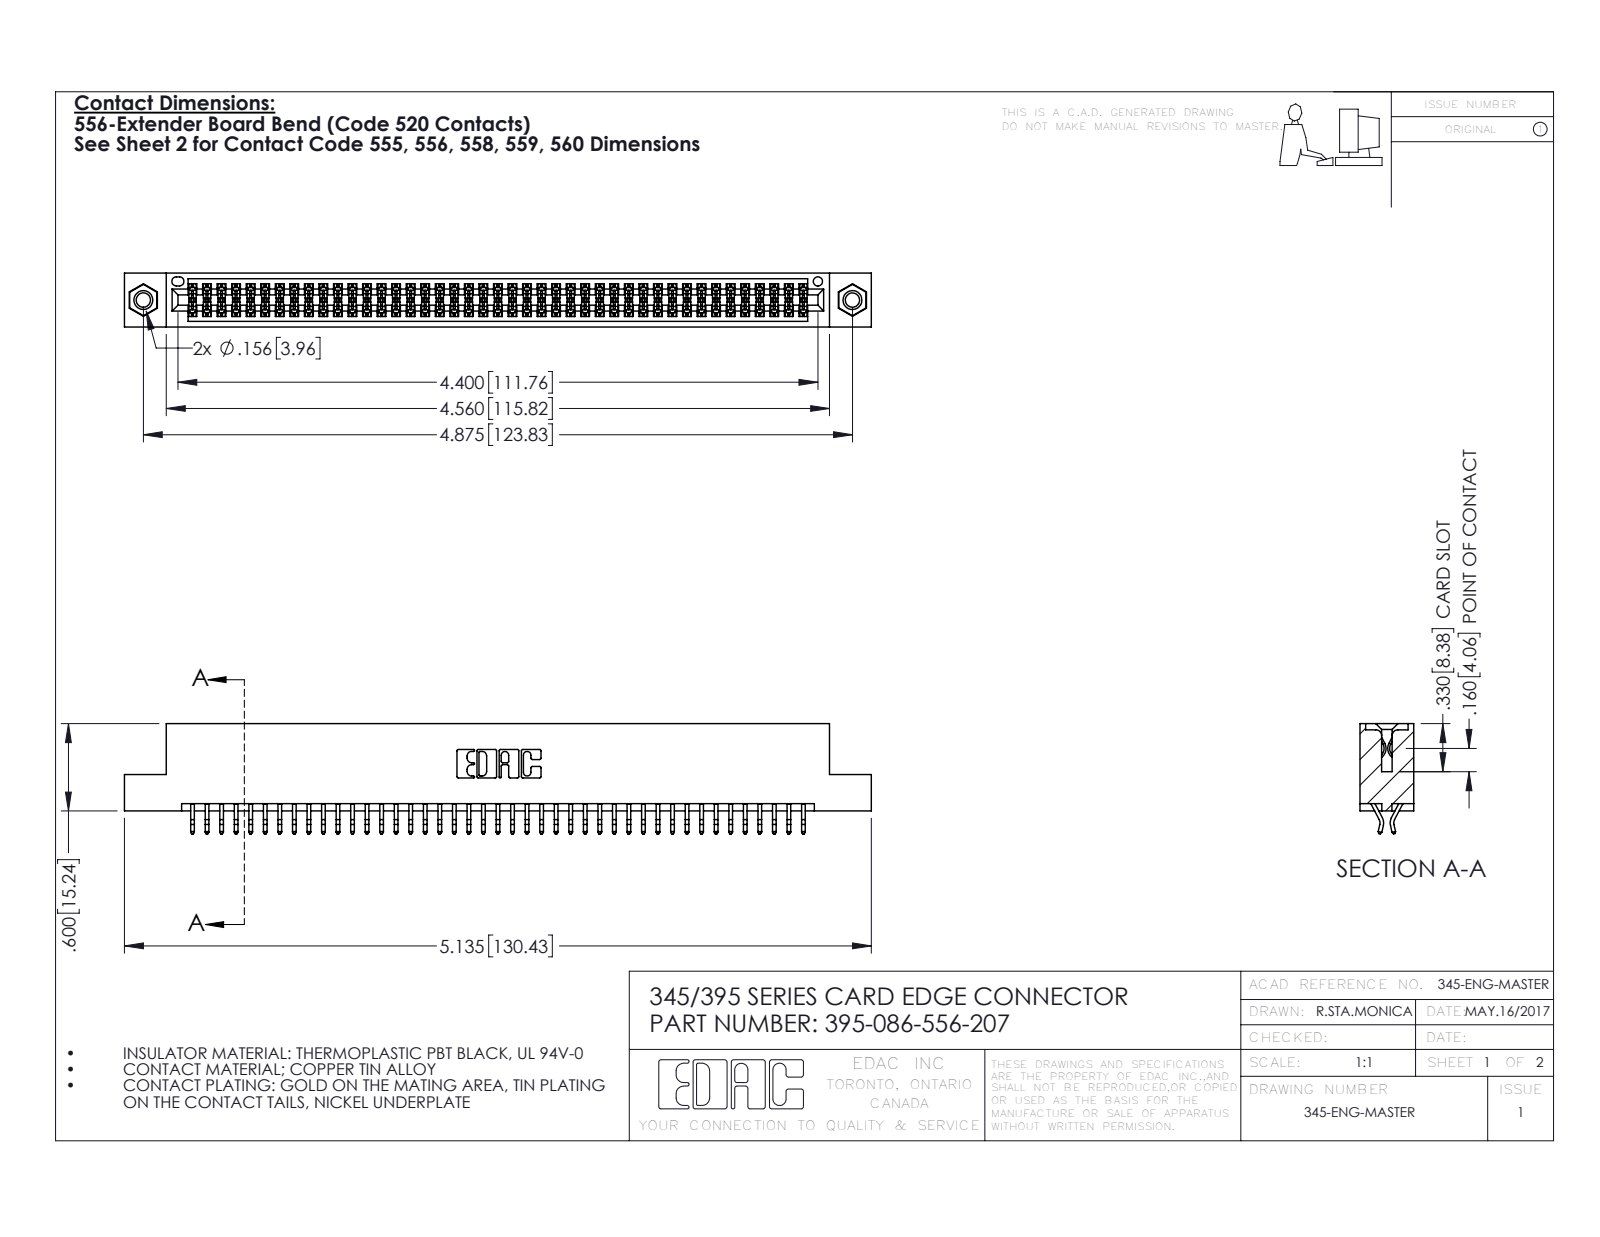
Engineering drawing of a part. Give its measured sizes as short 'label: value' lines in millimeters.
name: 345-292-001_556 Tail; 345-250-001_345-250-005-103; 395-086-556-207; 345 Part_Flush Mounting Lugs - 0.156 Dia-TI
written by: SolidWorks 2016 (CONFIG_CONTROL_DESIGN)
unit: mm
bodies: 89 solids, 5002 faces (3294 planar, 1692 cylindrical, 16 other)
size: 130.4 × 19.2 × 9.4
volume: 12 700 mm³; area: 18 690 mm²
holes: 2× ⌀2.5, 2× ⌀3.2, 2× ⌀4, 1× ⌀1.6
bosses: 2× ⌀3.9
rounds: 129× R0.2, 22× R0.3, 6× R0.2, 6× R0.8, 3× R0.7, 2× R0.3, 2× R0.4, 2× R0.5
face distances: 1.8, 7.6, 9.4, 5.1, 0.6, 2.5, 6.9, 5.7, 4.4, 3.8
hole spacings: 6.9, 117.8, 123.8
